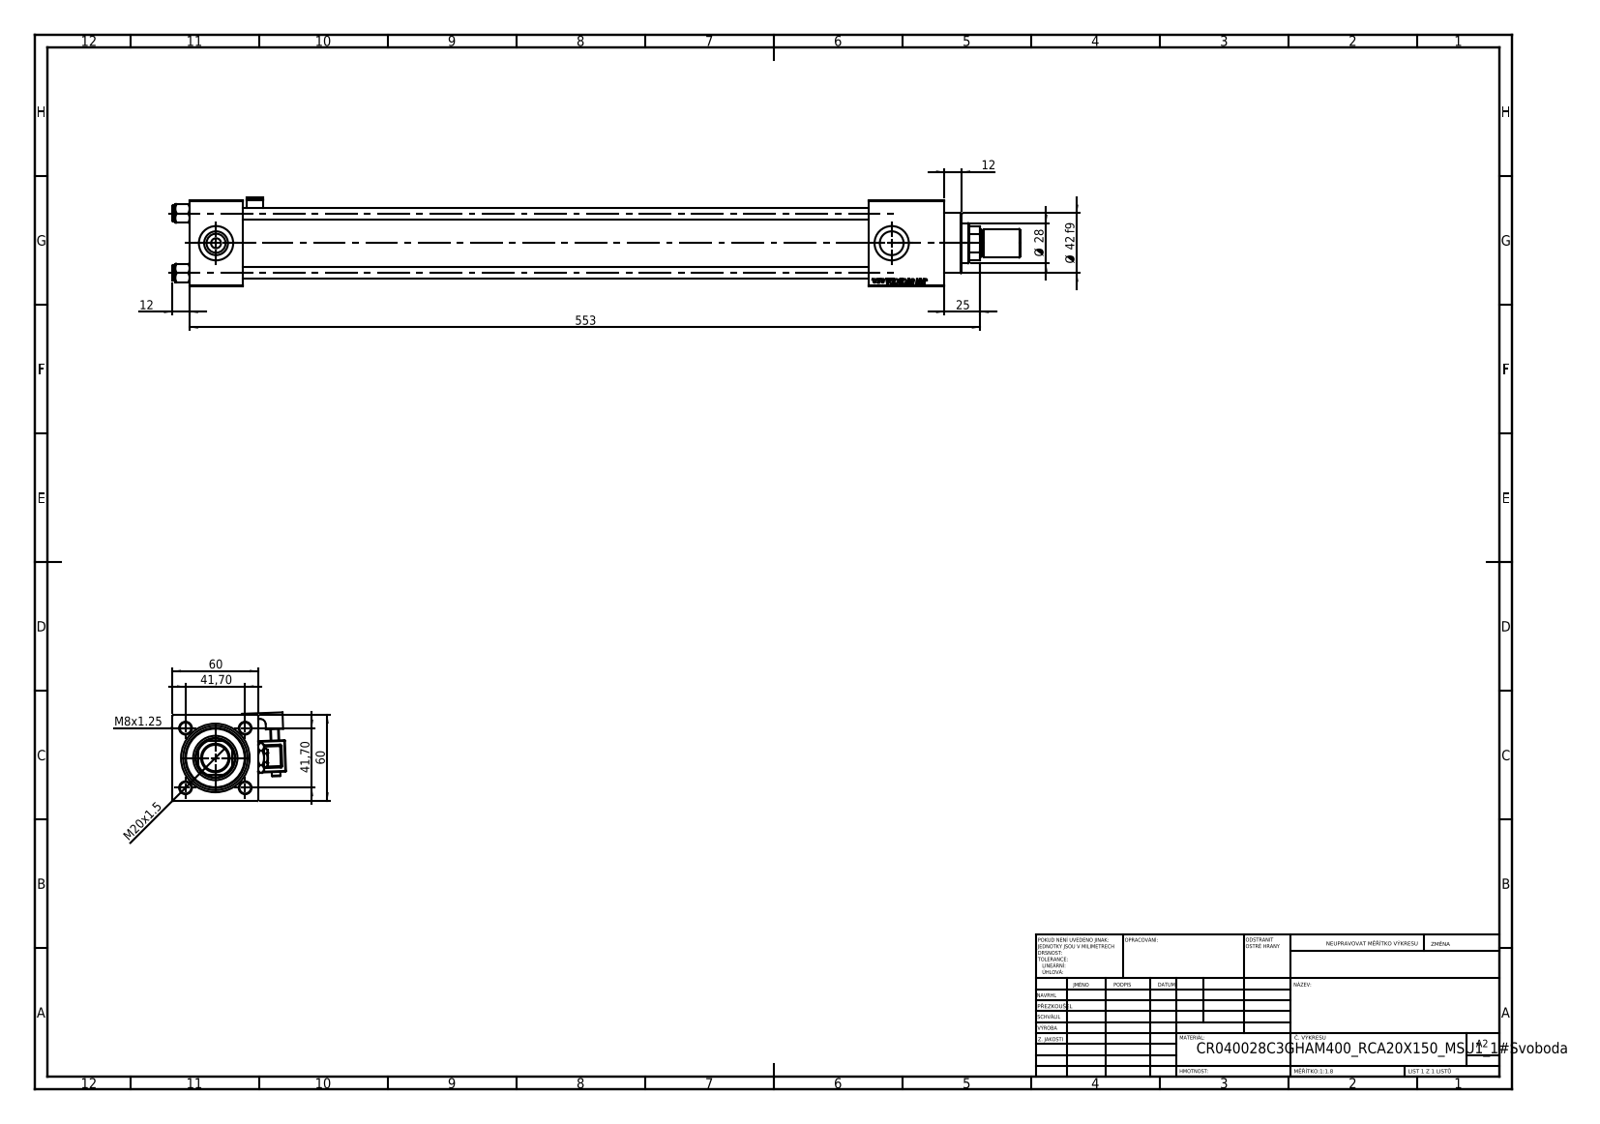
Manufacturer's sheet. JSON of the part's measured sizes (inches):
{"part_name": "V215_VC_A; V215CR_C_TYCINKA; V215CR_VCP_C; ROD_END_AH (+4 more)", "step_written_by": "SolidWorks 2019 (CONFIG_CONTROL_DESIGN)", "units": "inches", "bodies": {"solids": 15, "faces": 1341, "planar": 607, "cylindrical": 132, "other": 602}, "overall_size": [23.346, 3.127, 2.437], "volume_in3": 55.8, "surface_area_in2": 460.5, "round_holes": [[0.315, 4], [0.276, 2], [0.656, 2], [0.945, 2], [0.728, 1], [1.102, 1], [1.22, 1], [1.575, 1], [1.772, 1]], "round_bosses_or_shafts": [[0.433, 4], [1.811, 1], [1.654, 1], [0.787, 1], [0.709, 1], [0.236, 1]], "partial_cylinders_radius": [[0.02, 24], [0.039, 1], [0.098, 1], [0.157, 1], [0.531, 1]], "face_to_face_distances": [2.362, 1.457, 18.701, 17.244, 2.087, 19.657, 18.201, 0.957, 20.787, 19.331], "hole_center_spacings": [1.161, 1.642, 2.322, 18.602]}
